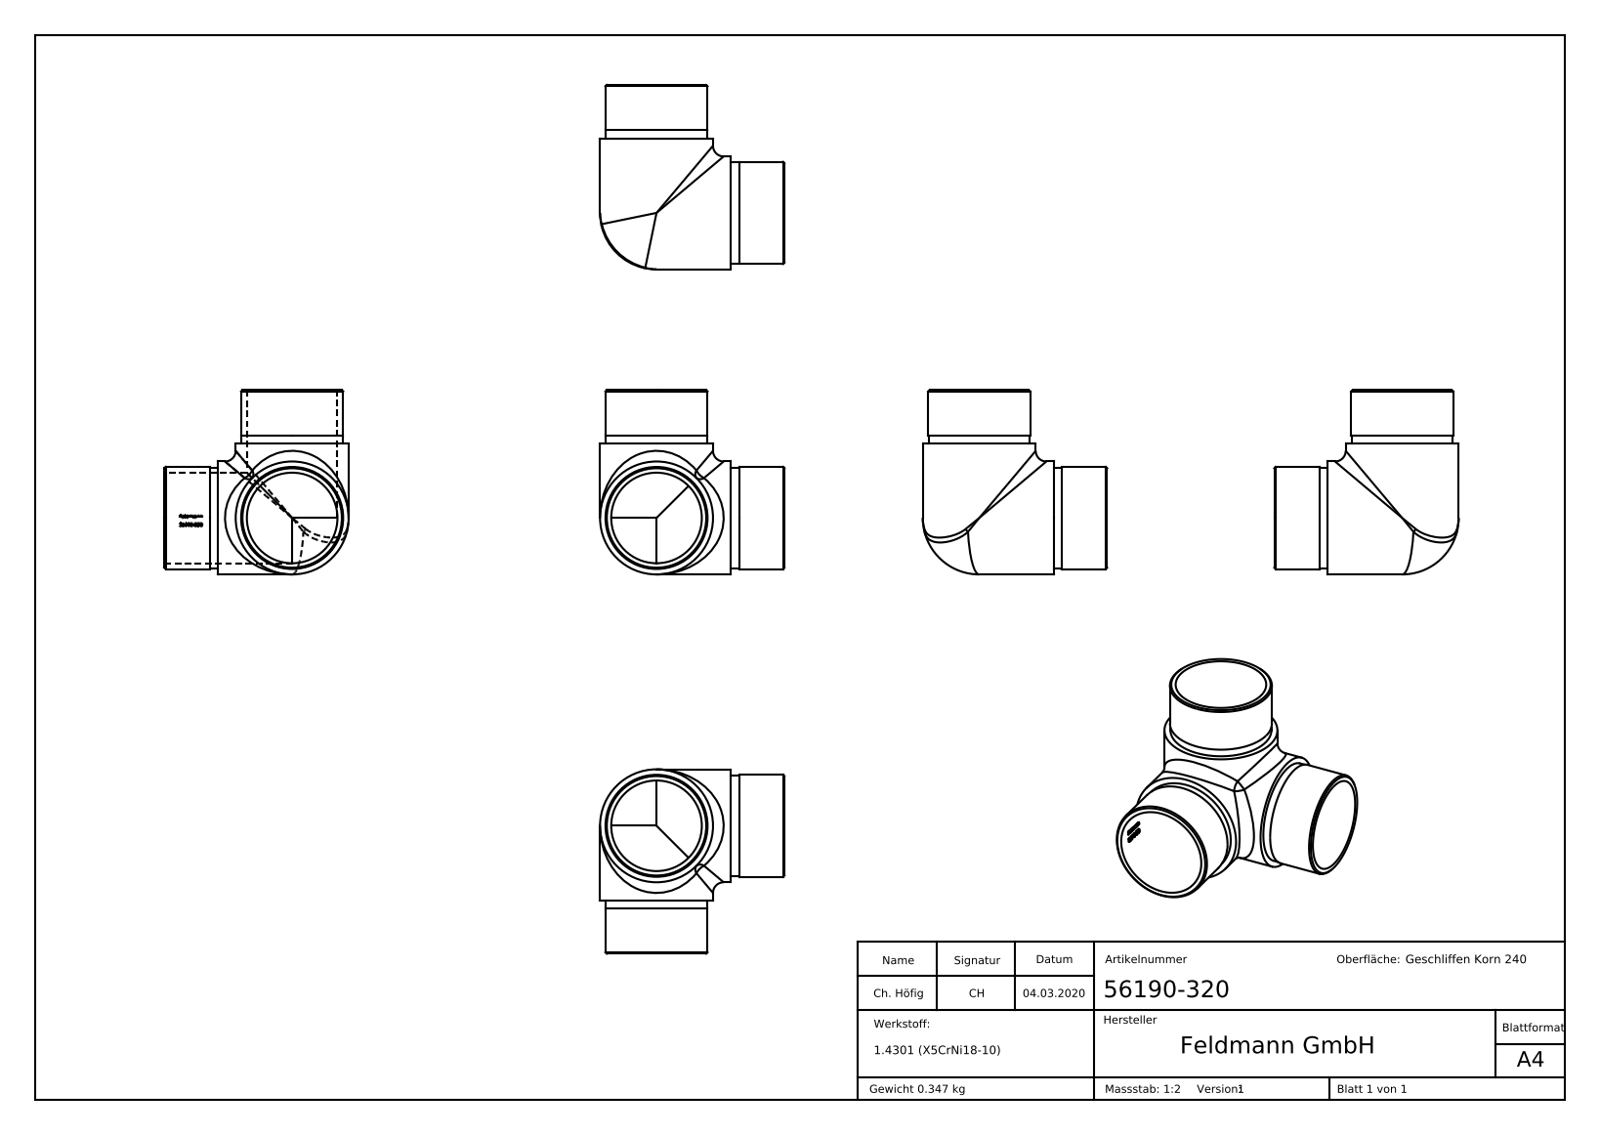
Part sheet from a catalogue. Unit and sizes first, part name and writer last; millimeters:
Units: millimetres
Overall size (bounding box): 69.2 × 69.2 × 69.2
Round holes (diameter × count): ⌀34 ×3
Round bosses / shafts (diameter × count): ⌀42.4 ×3, ⌀38.3 ×3, ⌀37.9 ×3
Partial cylindrical surfaces — rounded edges, fillets, slot ends (radius × count): R17.1 ×1
Main face-to-face distances: 20, 3, 17, 0.39, 1.26, 2.97, 4.23, 1.32, 3.66, 3.27
Volume: 43 985 mm³ · Surface area: 28 853 mm²
Bodies: 1 solid, 254 faces (94 planar, 36 cylindrical, 124 other)
Part name (STEP PRODUCT): 56190-320
STEP written by: SolidWorks 2015 (CONFIG_CONTROL_DESIGN)
